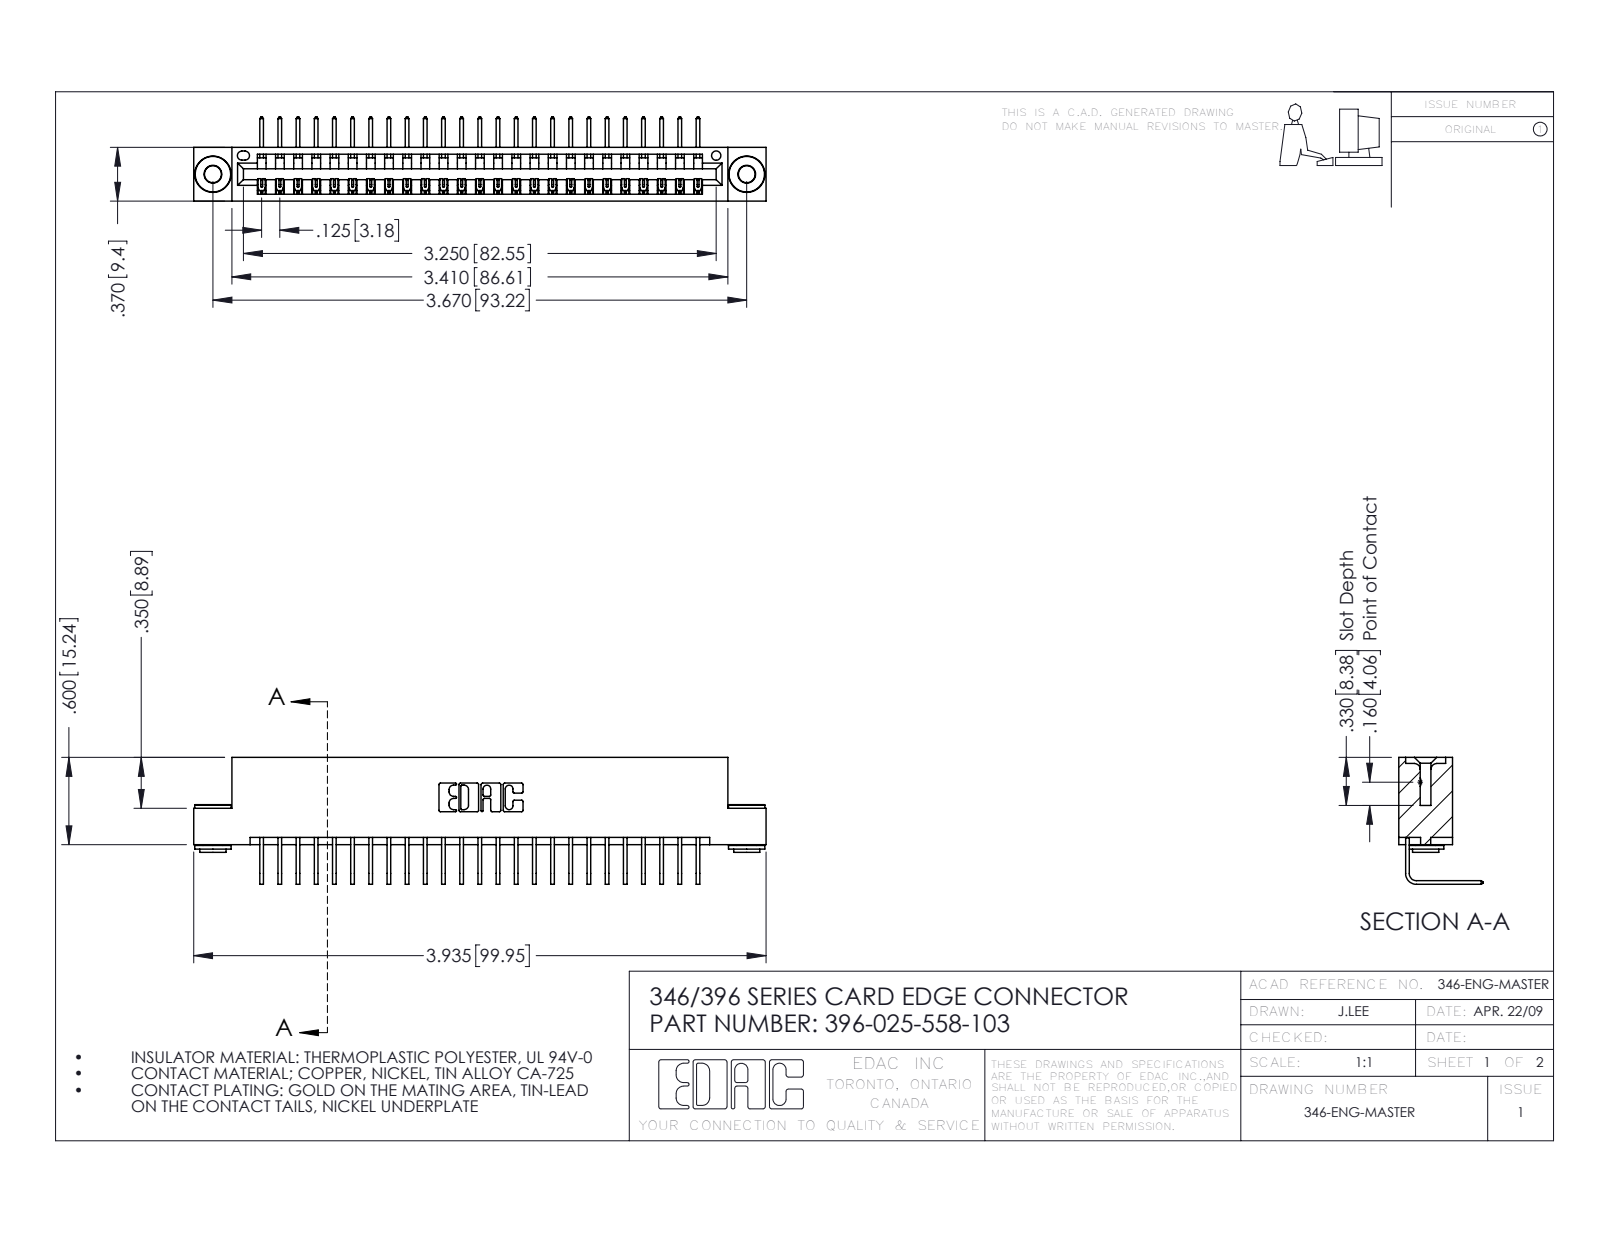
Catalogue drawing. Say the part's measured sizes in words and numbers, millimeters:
The part is named "345-292-001_558 Tail - 2; 345-250-002_345-250-002-102; 346 Part_Flush Mounting Lugs - 0.156 Dia-TH; 396-025-558-103". Its 3-D file was written by "SolidWorks 2016 (CONFIG_CONTROL_DESIGN)". It is 28 solids with 1660 faces: 1136 planar, 516 cylindrical and 8 other. Overall it measures 99.9 by 22.2 by 14.7 millimeters. Its volume is 9 550 cubic millimeters and its surface area 12 470 square millimeters. Round holes: 2 of diameter 2.9, 2 of diameter 4, 1 of diameter 1.6. Round bosses or shafts: 2 of diameter 6.4, 2 of diameter 4.6, 2 of diameter 3.5. Partial cylindrical surfaces (rounded edges, fillets, slot ends): 50 of radius 0.2, 22 of radius 0.3, 6 of radius 0.2, 6 of radius 0.8, 3 of radius 0.7, 2 of radius 0.8, 2 of radius 1, 1 of radius 0.4. The main face-to-face distances are 8.2, 1.2, 9.4, 6.4, 0.6, 7.6, 1.8, 3.8, 5.6, 2.5. The hole center spacings are 6.2, 87.9, 93.2.
